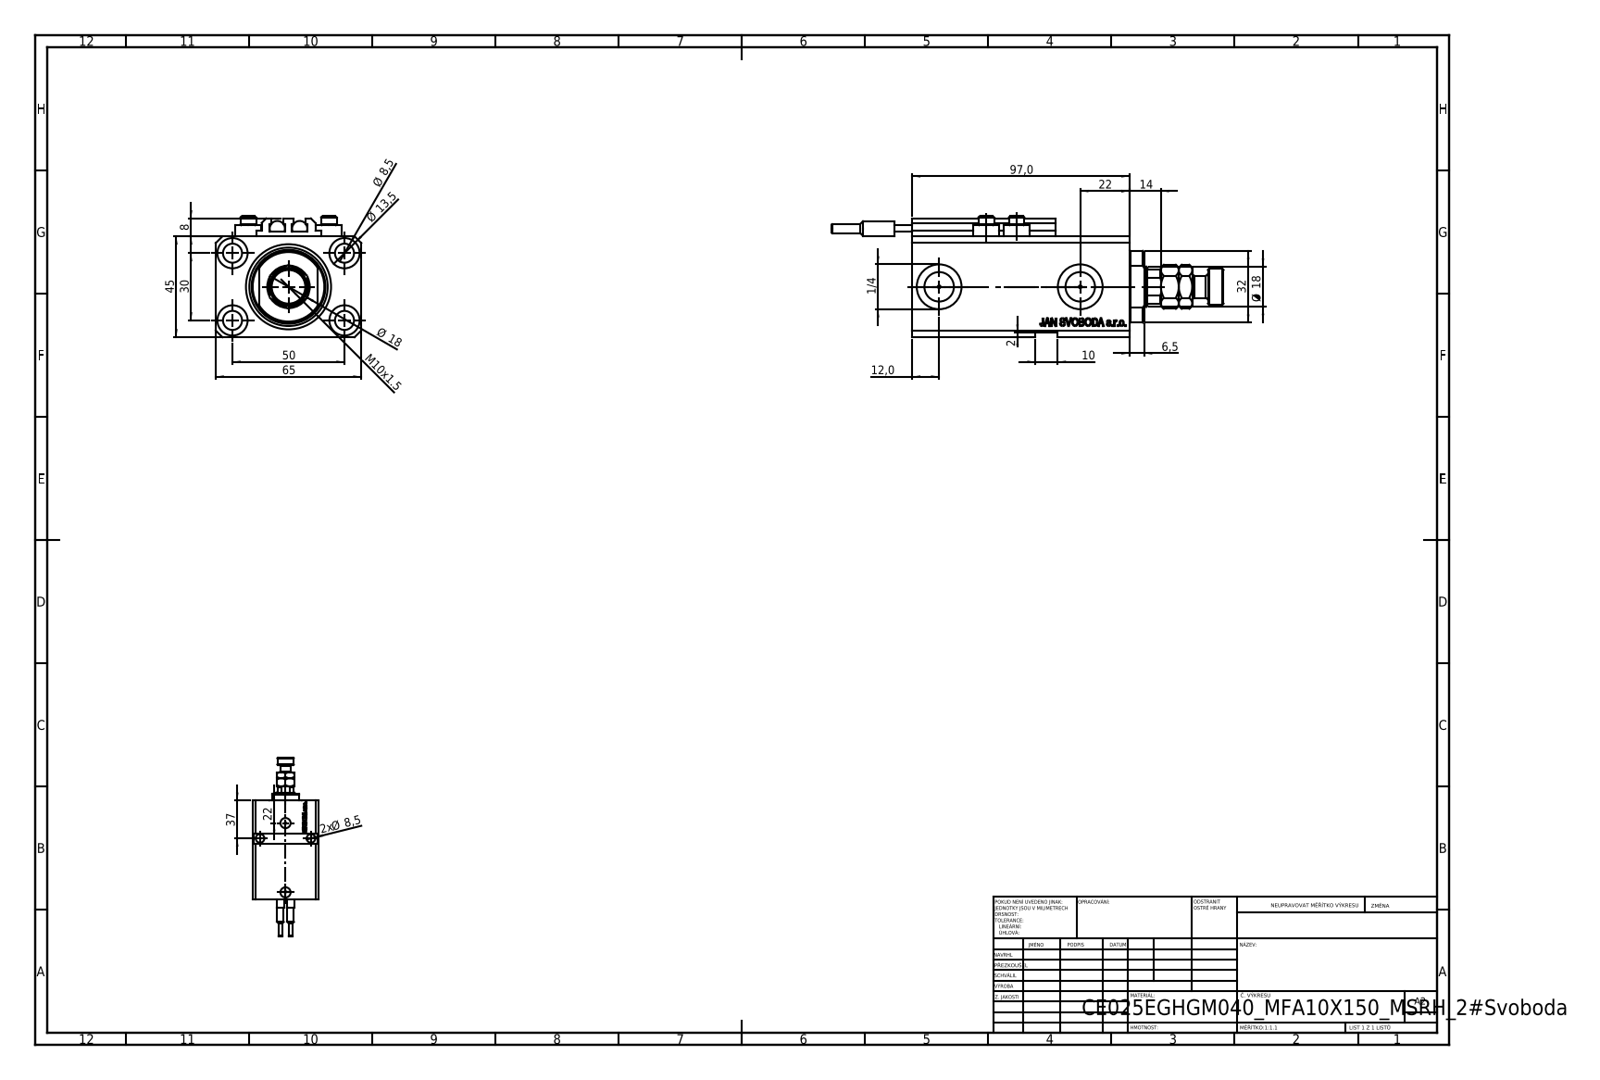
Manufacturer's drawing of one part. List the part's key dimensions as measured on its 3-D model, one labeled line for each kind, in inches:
Part name (STEP PRODUCT): V250CE_VC_E; V250CE_C_VCP; MFA; SWITCH_V250CE (+2 more)
STEP written by: SolidWorks 2019 (CONFIG_CONTROL_DESIGN)
Units: inches
Bodies: 11 solids, 1171 faces (559 planar, 142 cylindrical, 470 other)
Overall size (bounding box): 6.89 × 2.559 × 2.126
Volume: 15.88 in³ · Surface area: 116.4 in²
Round holes (diameter × count): ⌀0.335 ×7, ⌀0.049 ×4, ⌀0.157 ×4, ⌀0.531 ×4, ⌀0.394 ×2, ⌀0.518 ×2, ⌀0.787 ×2, ⌀0.709 ×1, ⌀0.984 ×1, ⌀1.496 ×1
Round bosses / shafts (diameter × count): ⌀0.457 ×4, ⌀0.276 ×4, ⌀0.268 ×2, ⌀0.256 ×2, ⌀0.157 ×2, ⌀0.63 ×1, ⌀0.394 ×1
Partial cylindrical surfaces — rounded edges, fillets, slot ends (radius × count): R0.008 ×10, R0.335 ×1, R0.63 ×1
Main face-to-face distances: 1.772, 2.559, 0.551, 0.079, 1.85, 3.268, 0.118, 3.819, 0.272, 0.197
Hole centre spacings: 1.148, 1.969, 0.535, 0.595, 1.098, 1.181, 1.228, 1.245
